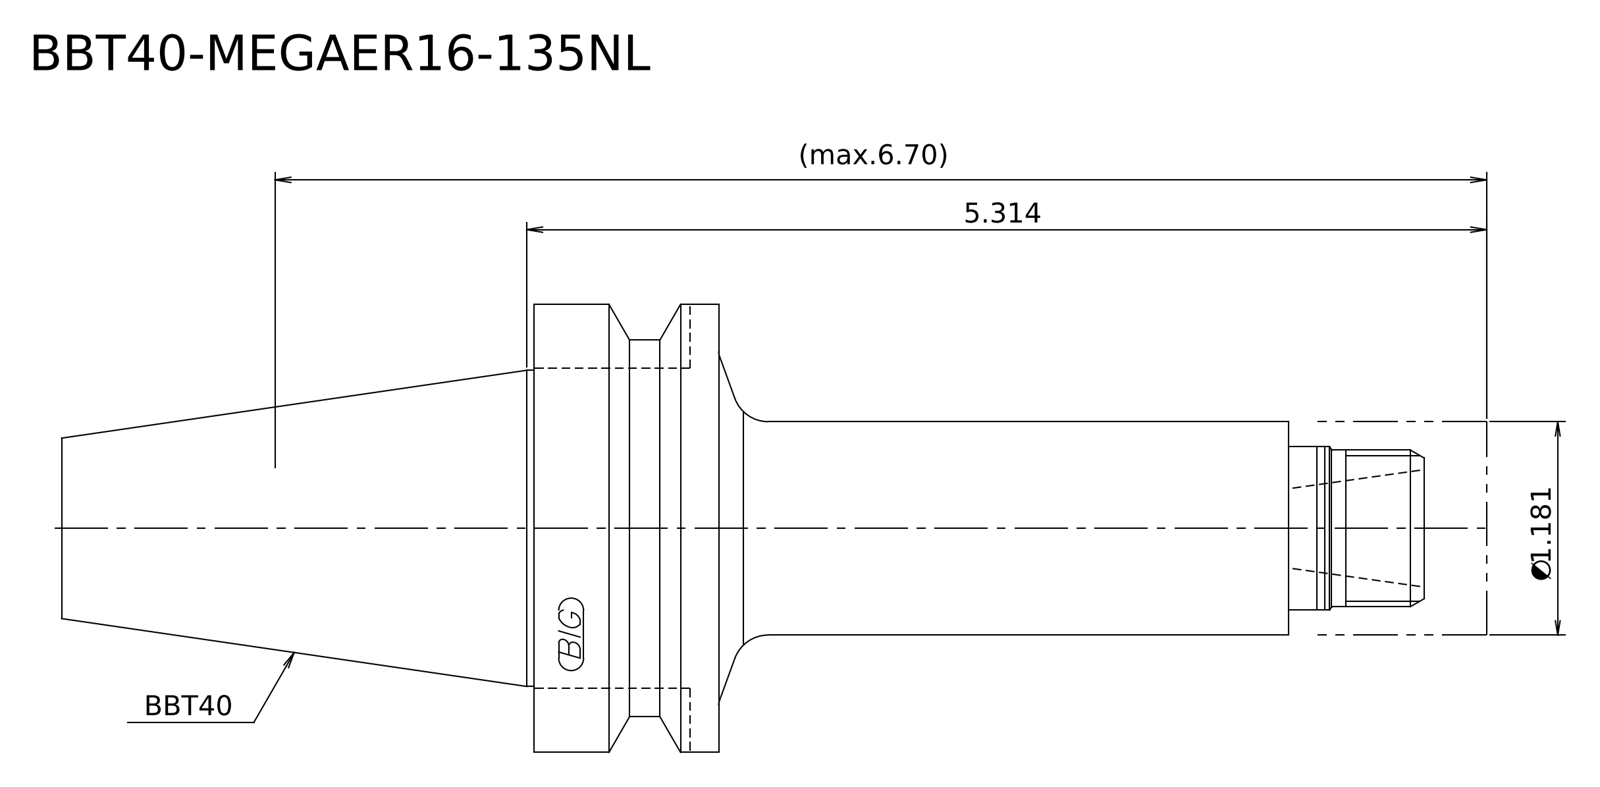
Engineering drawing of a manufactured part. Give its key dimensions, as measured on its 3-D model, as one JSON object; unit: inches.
{"step_written_by": "Kubotek KeyCreator 2011 V10.0.2 (22737) (automotive_design)", "units": "inches", "bodies": {"solids": 2, "faces": 21, "planar": 7, "cylindrical": 8, "other": 6}, "overall_size": [7.89, 2.48, 2.48], "volume_in3": 13.78, "surface_area_in2": 47.67, "round_bosses_or_shafts": [[2.48, 1], [2.087, 1], [1.75, 1], [1.181, 1], [0.906, 1], [0.866, 1]], "face_to_face_distances": [1.024, 3.268, 4.291, 0.984, 4.252, 5.276, 7.89, 6.906, 3.638, 2.614]}
